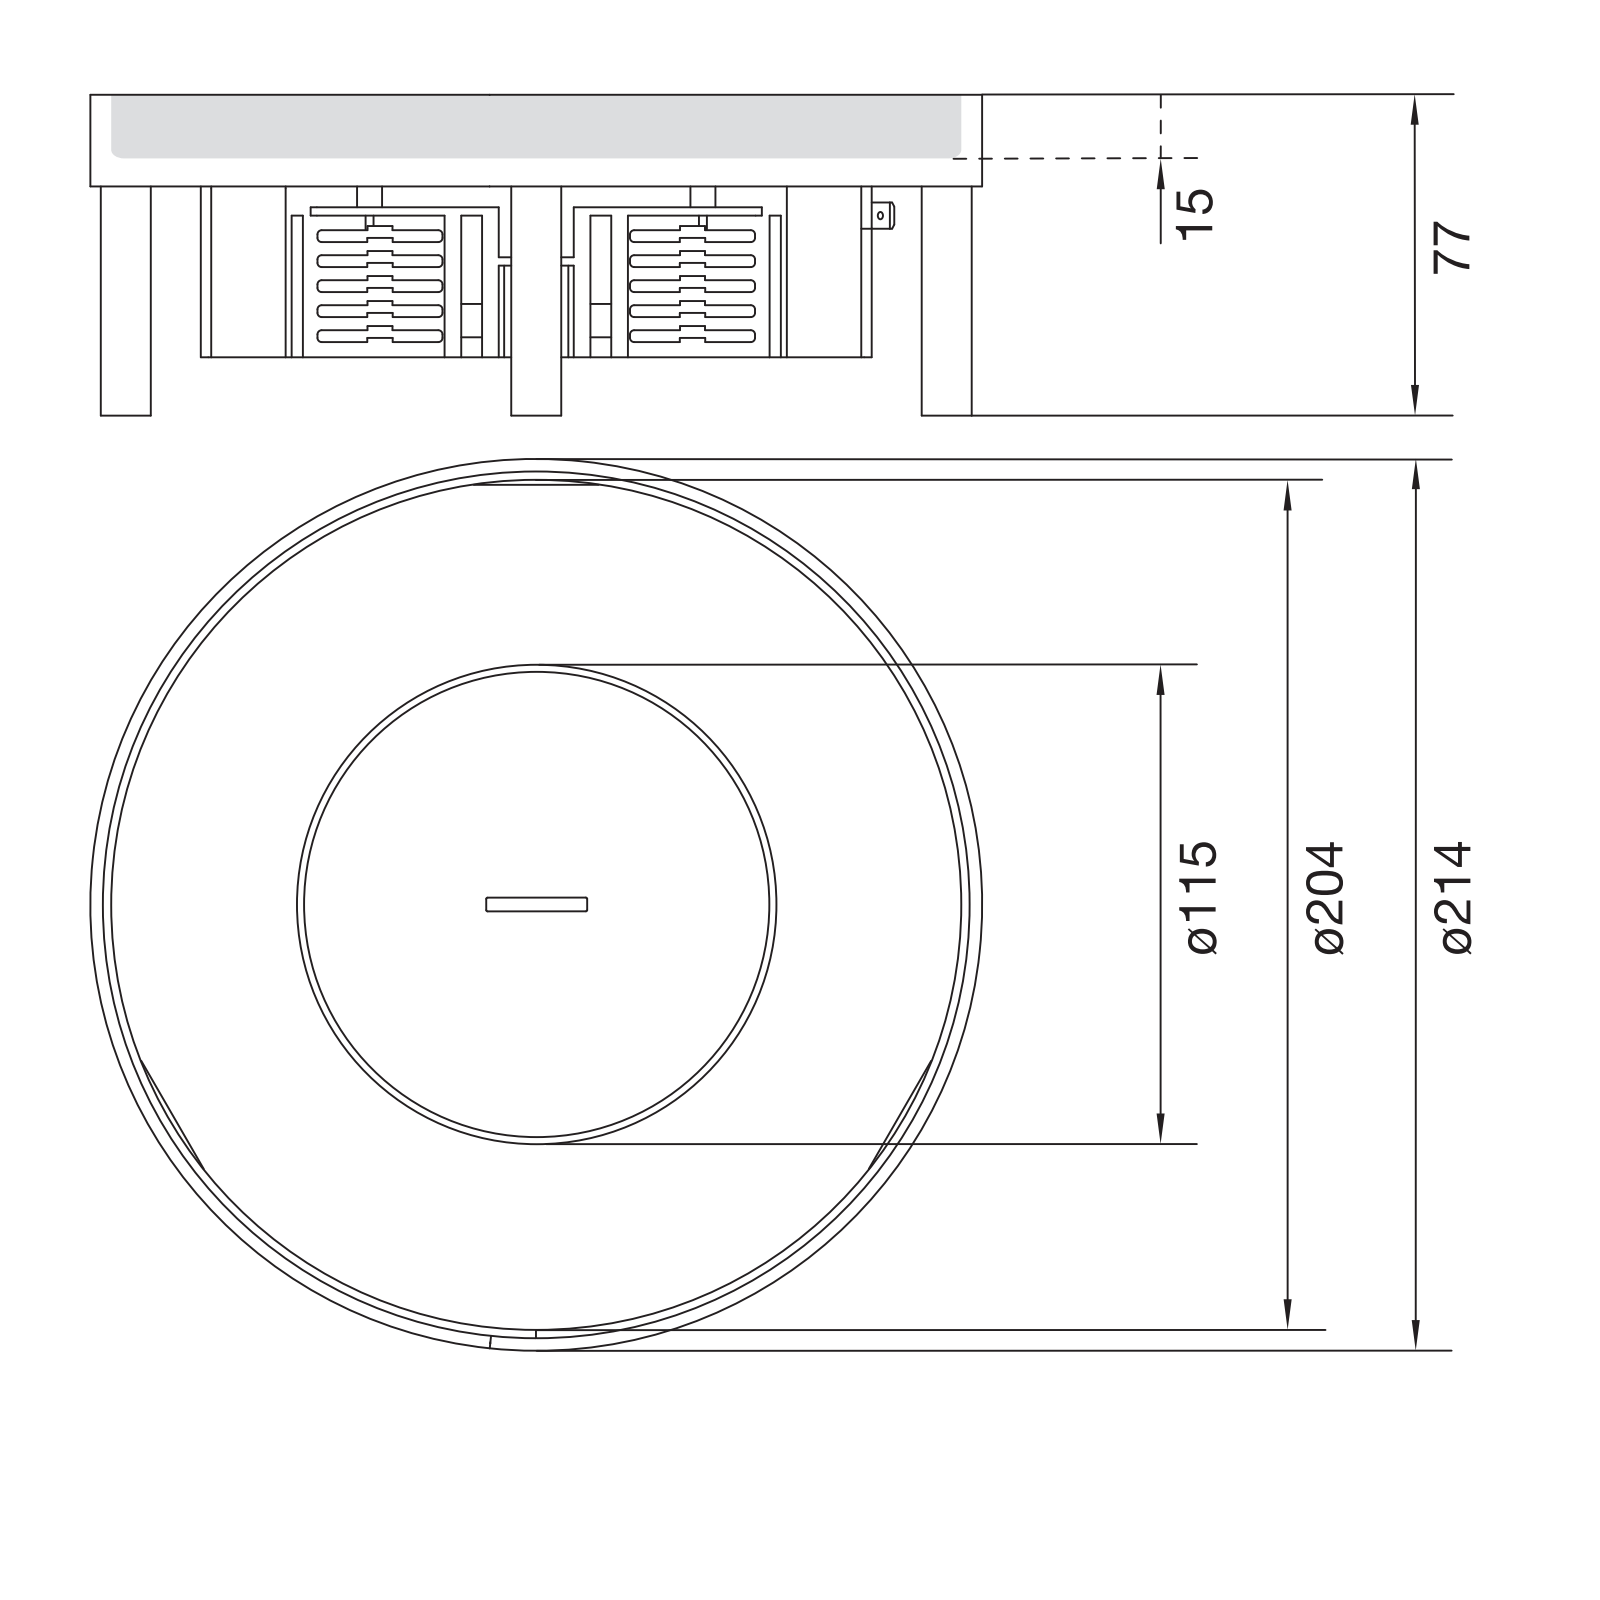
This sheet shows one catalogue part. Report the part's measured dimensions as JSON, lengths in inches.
{"part_name": "T-00671; T-00672; T-00673; T-00674 (+8 more)", "step_written_by": "CREO PARAMETRIC BY PTC INC, 2022024 (AUTOMOTIVE_DESIGN)", "units": "inches", "bodies": {"solids": 15, "faces": 228, "planar": 109, "cylindrical": 109, "other": 10}, "overall_size": [8.425, 8.425, 3.031], "volume_in3": 16.05, "surface_area_in2": 395.3, "round_holes": [[0.15, 6], [0.268, 4], [0.335, 4], [0.398, 4], [0.177, 3], [3.173, 1], [3.543, 1], [3.976, 1], [4.213, 1], [4.276, 1], [4.409, 1], [4.425, 1]], "round_bosses_or_shafts": [[0.472, 4], [0.388, 4], [8.425, 1], [8.189, 1], [8.031, 1], [4.528, 1], [4.37, 1], [4.134, 1]], "partial_cylinders_radius": [[0.02, 8], [0.197, 3], [1.693, 1]], "face_to_face_distances": [0.079, 0.098, 0.197, 0.591, 0.669, 6.043, 0.276, 0.866, 0.787, 0.118], "hole_center_spacings": [1.62, 3.834, 3.878, 4.187, 5.484, 6.477, 7.54, 2.126]}
